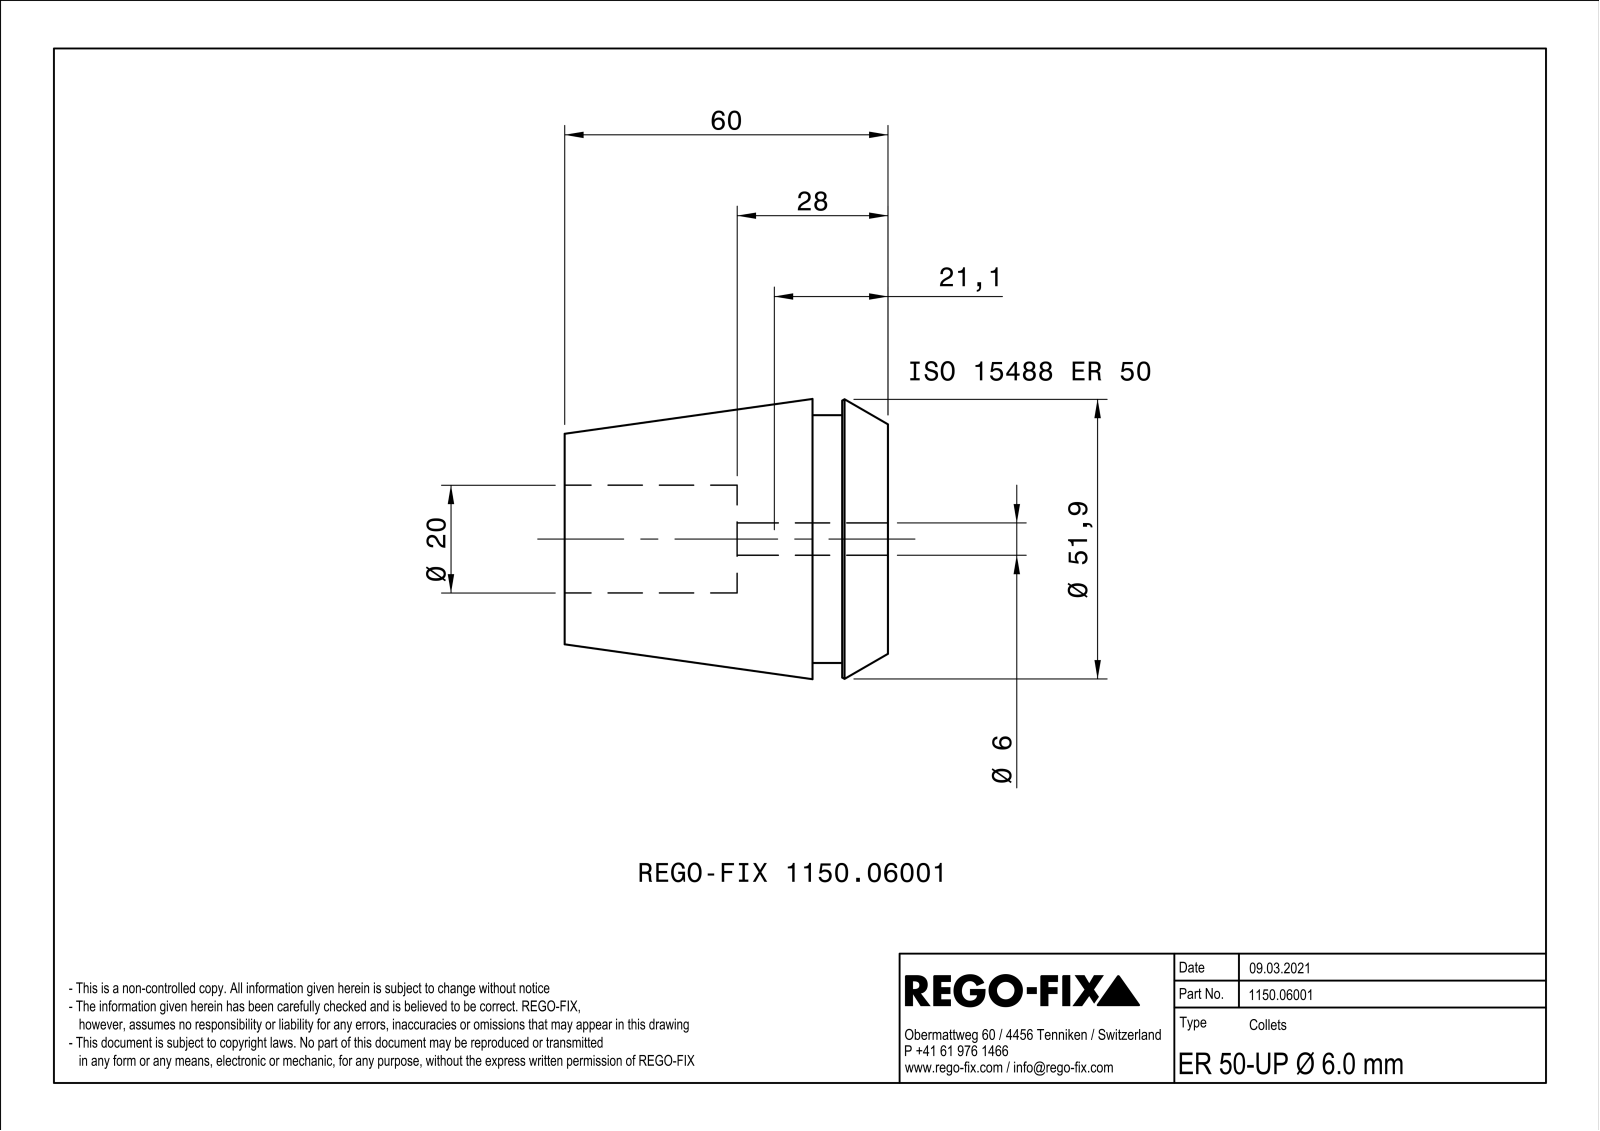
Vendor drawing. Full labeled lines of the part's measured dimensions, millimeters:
Part name (STEP PRODUCT): NOCUT
STEP written by: SIEMENS PLM Software Solid Edge ST10 (AUTOMOTIVE_DESIGN)
Units: millimetres
Bodies: 1 solid, 275 faces (121 planar, 25 cylindrical, 129 other)
Overall size (bounding box): 60 × 51.99 × 51.99
Volume: 76 157 mm³ · Surface area: 38 415 mm²
Round holes (diameter × count): ⌀6 ×1, ⌀20 ×1
Round bosses / shafts (diameter × count): ⌀46 ×1
Main face-to-face distances: 1, 1.02, 0.98, 60, 14, 46, 8.5, 5.5, 51.5, 28
